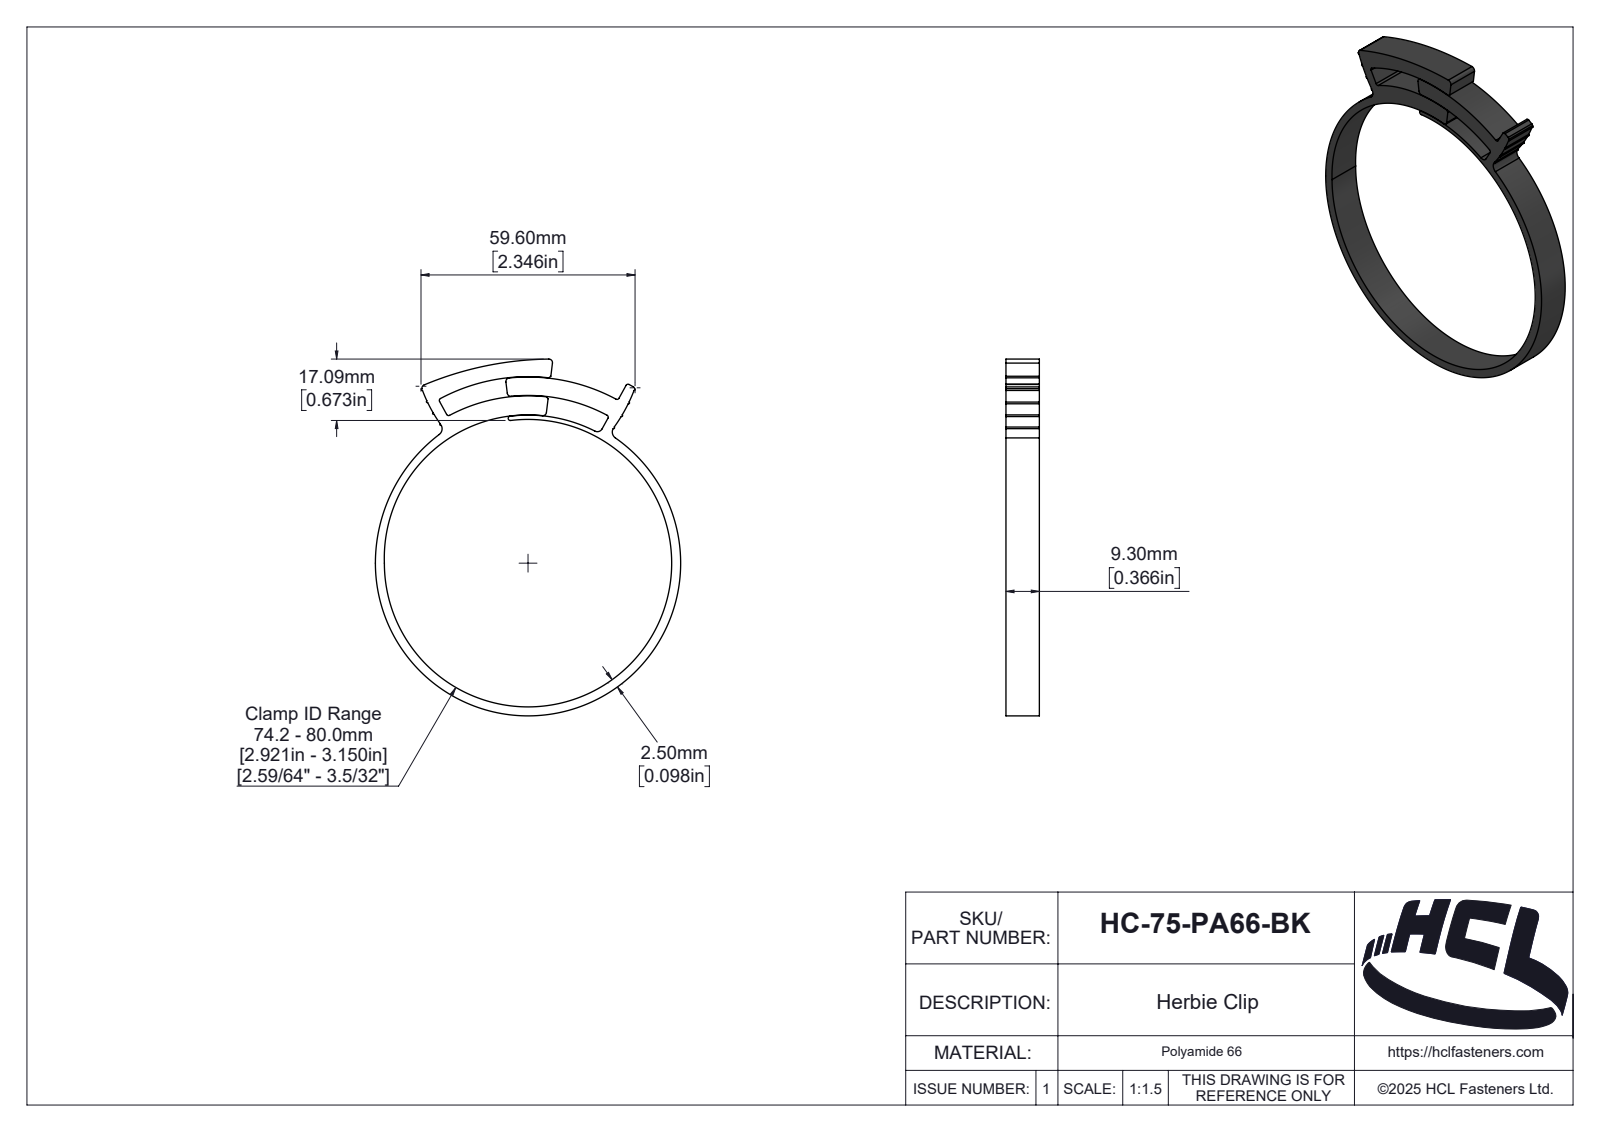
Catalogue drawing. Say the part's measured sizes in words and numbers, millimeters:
The part is named "HC-75-PA66-BK". Its 3-D file was written by "SolidWorks 2025 (AUTOMOTIVE_DESIGN)". It is 1 solid with 162 faces: 13 planar, 100 cylindrical and 49 other. Overall it measures 99.29 by 85 by 9.3 millimeters. Its volume is 10 315 cubic millimeters and its surface area 9 006 square millimeters. Partial cylindrical surfaces (rounded edges, fillets, slot ends): 8 of radius 0.25, 7 of radius 0.6, 5 of radius 1, 2 of radius 2, 1 of radius 0.17, 1 of radius 0.67, 1 of radius 0.84, 1 of radius 0.89. The main face-to-face distances are 9.3.
